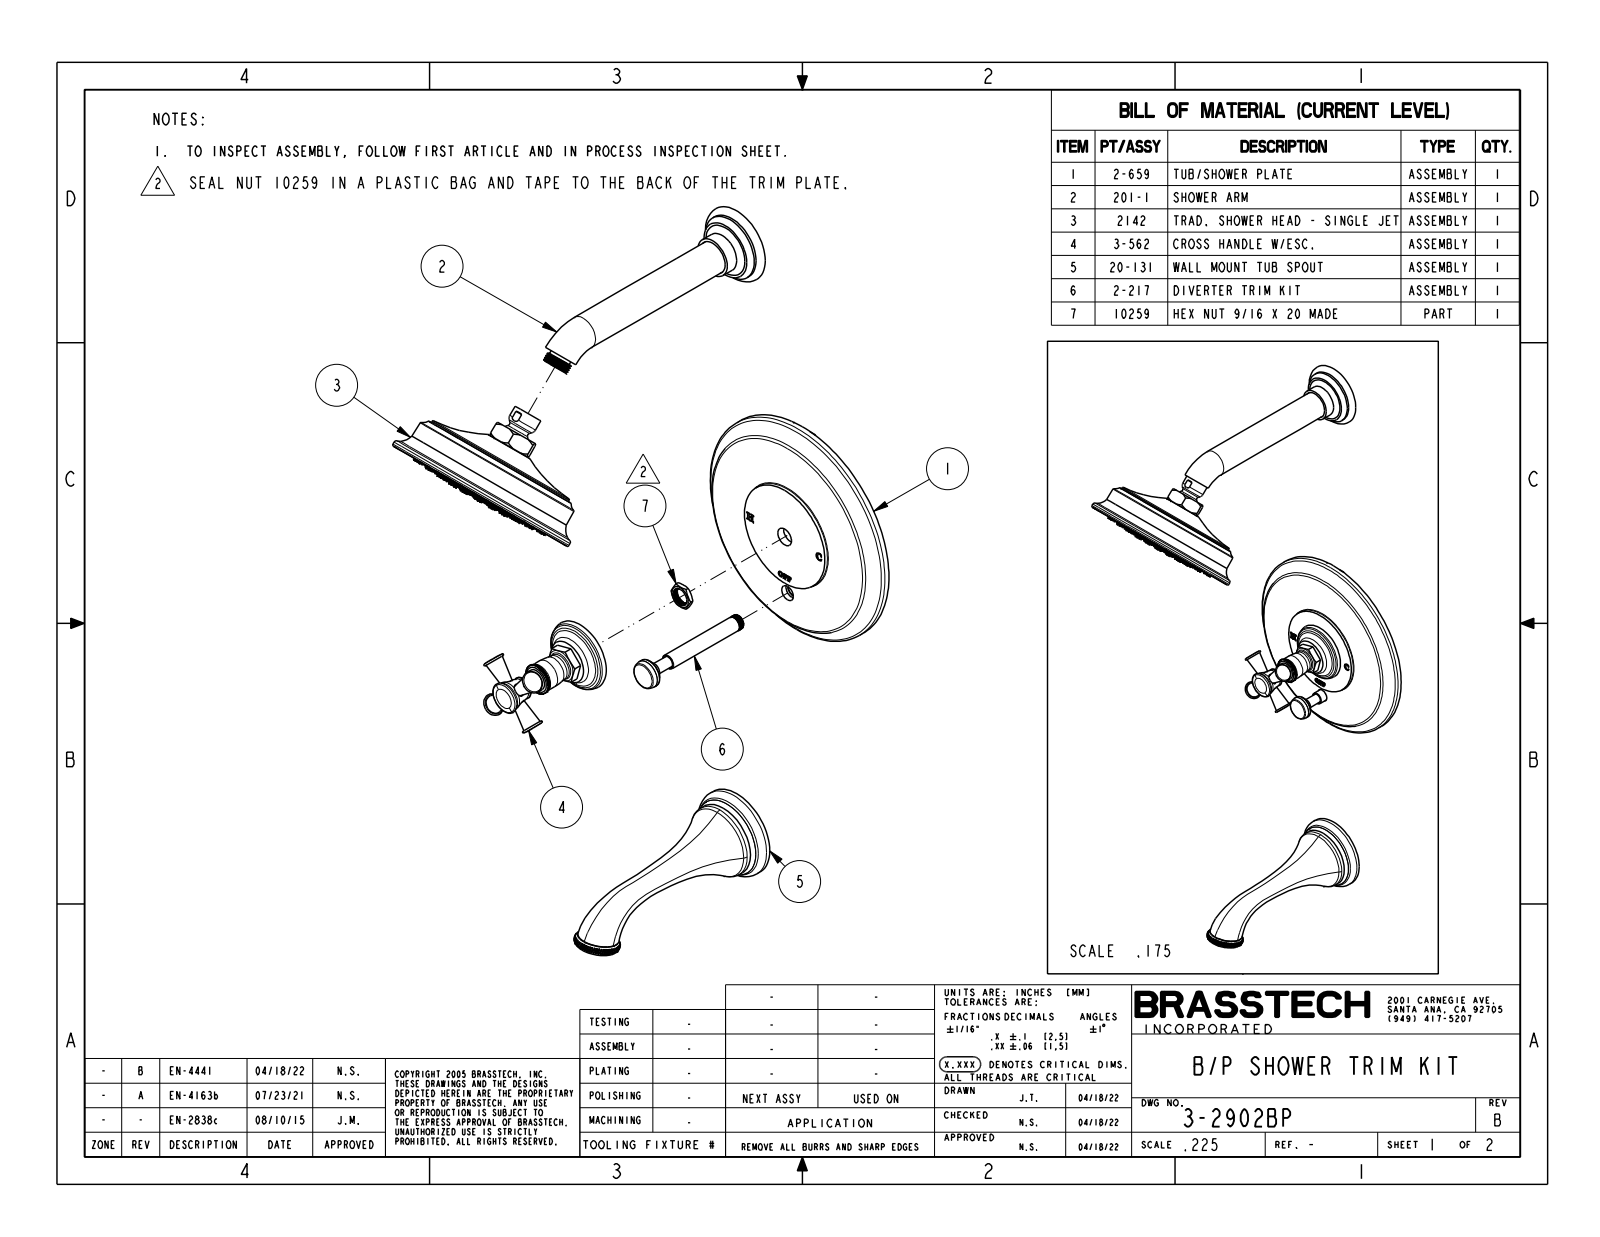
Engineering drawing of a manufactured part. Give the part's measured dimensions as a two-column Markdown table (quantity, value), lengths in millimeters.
| quantity | value |
| --- | --- |
| part name | 3-2902BP |
| STEP written by | CREO PARAMETRIC BY PTC INC, 2018400 (AUTOMOTIVE_DESIGN) |
| units | millimeters |
| bodies | 42 solids, 2219 faces (796 planar, 569 cylindrical, 854 other) |
| overall size | 626.8 × 304.7 × 190.5 |
| volume | 1 069 000 mm³ |
| surface area | 210 000 mm² |
| round holes (diameter × count) | 1.3 × 90, 3.2 × 90, 12.7 × 2, 3.8 × 1, 4.7 × 1, 5.6 × 1, 6.7 × 1, 8.8 × 1, 10 × 1, 15 × 1, 15.2 × 1, 15.3 × 1 |
| round bosses / shafts (diameter × count) | 5 × 60, 190.5 × 1, 157.5 × 1, 122.7 × 1, 72.4 × 1, 63.7 × 1, 59.6 × 1, 53.6 × 1 |
| main face-to-face distances | 3.2, 12.7, 15.9, 6.4, 3.2, 19.1, 0.4, 12.3, 18.7, 15.5 |
| hole center spacings | 46.7, 12.2, 46.7, 24.2, 57.7, 12, 35.8, 56.9 |
